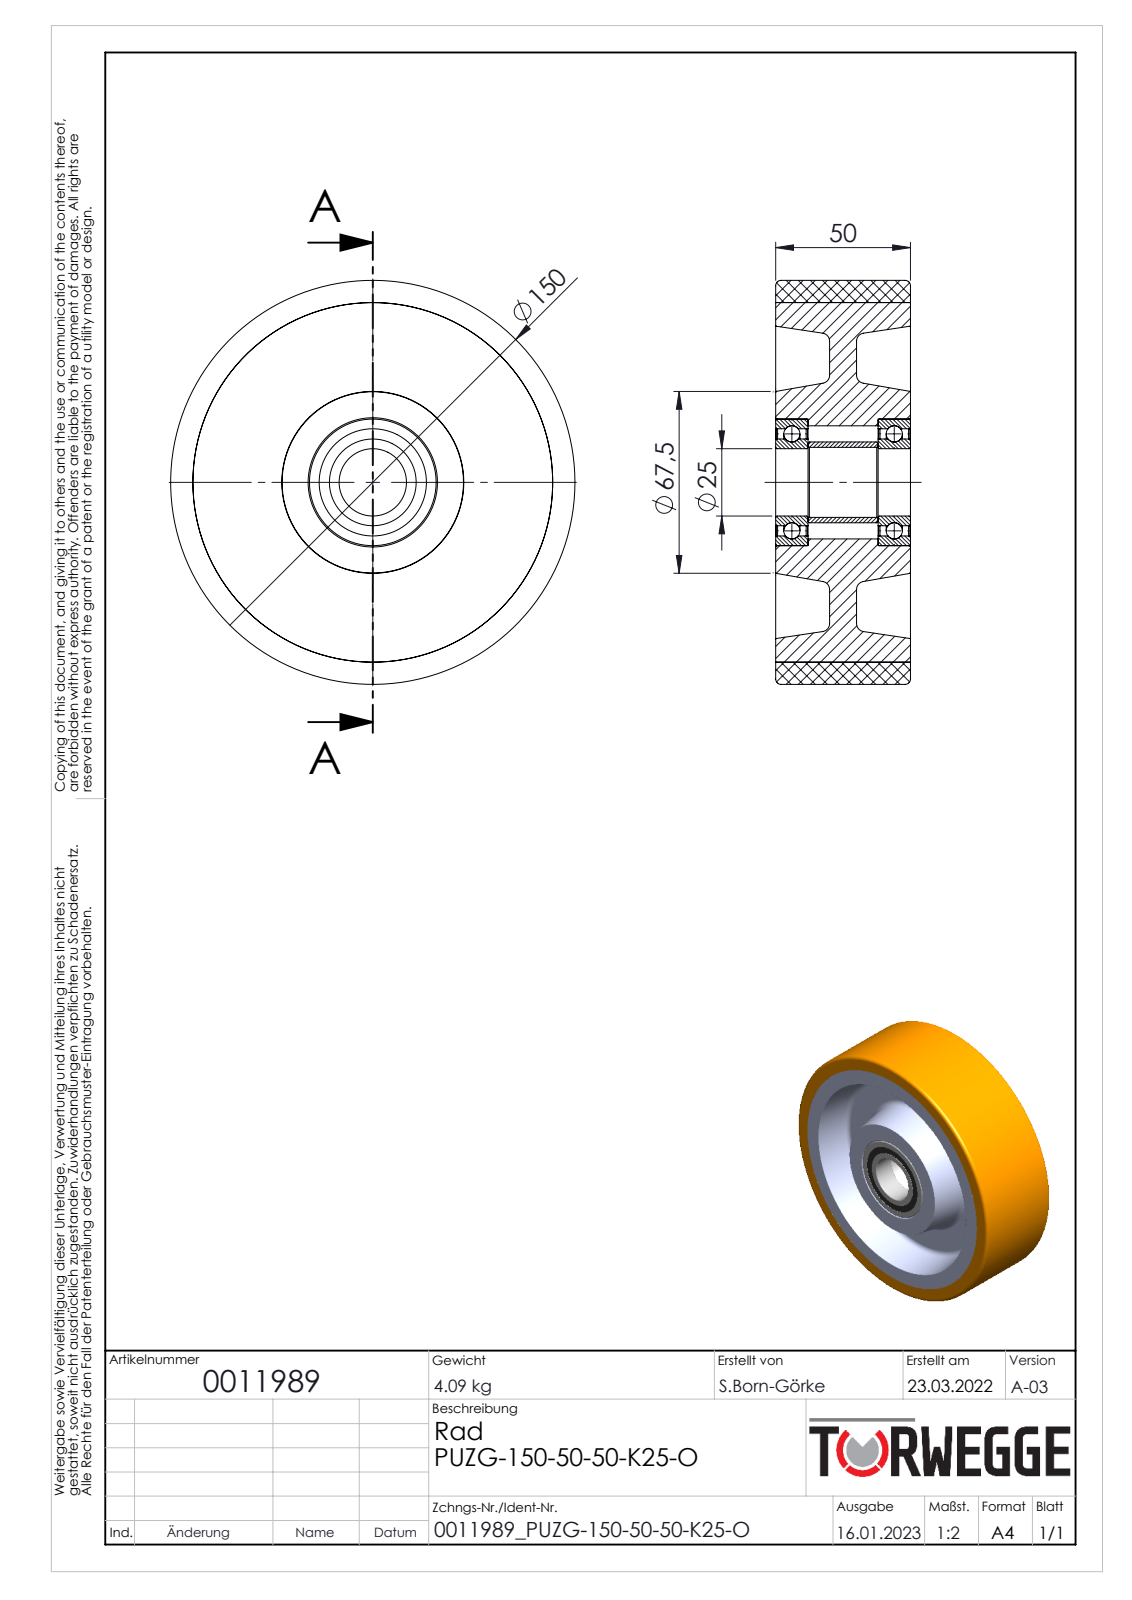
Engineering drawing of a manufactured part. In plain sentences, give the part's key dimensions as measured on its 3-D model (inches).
The part is named "0011989". Its 3-D file was written by "SolidWorks 2020 (AUTOMOTIVE_DESIGN)". It is 0 solids with 82 faces: 14 planar, 20 cylindrical and 48 other. Overall it measures 5.906 by 5.906 by 1.969 inches. Round holes: 1 of diameter 0.984, 1 of diameter 1.024, 1 of diameter 1.567, 1 of diameter 5.256. Round bosses or shafts: 1 of diameter 5.906, 1 of diameter 1.268. The main face-to-face distances are 1.969, 0.787, 1.181, 0.394, 1.961, 0.78, 1.173, 1.953.
